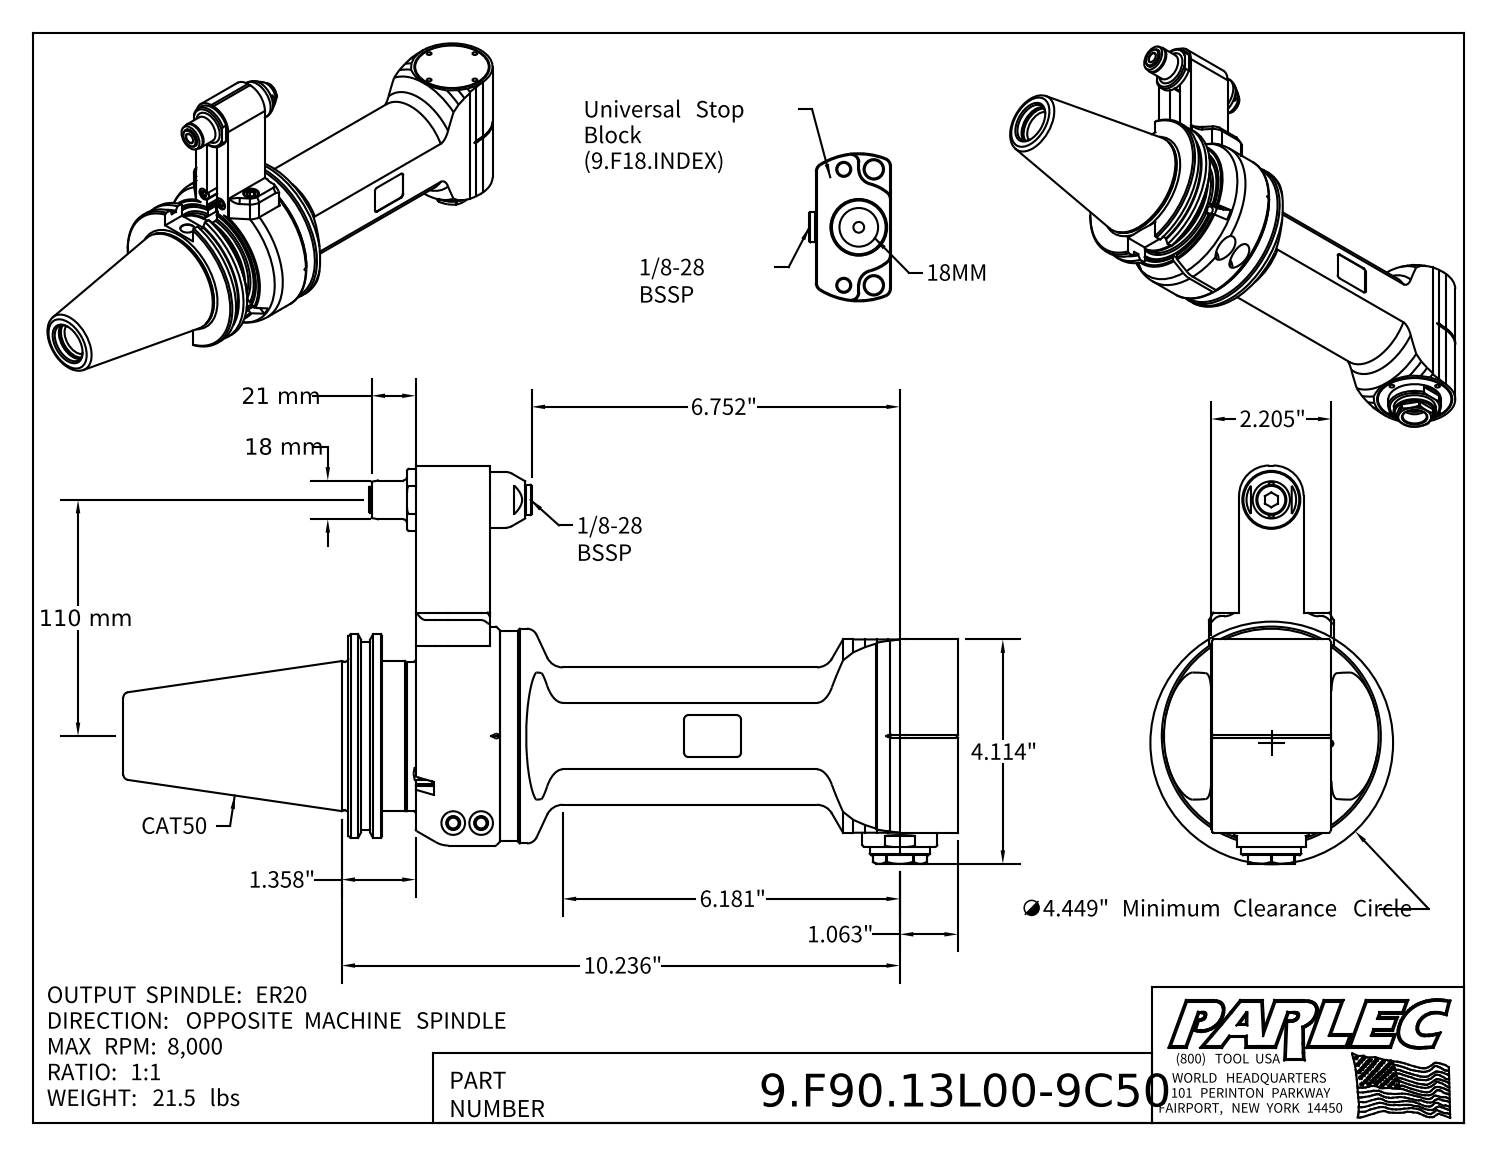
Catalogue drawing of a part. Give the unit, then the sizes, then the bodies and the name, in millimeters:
Units: millimetres
Overall size (bounding box): 388.6 × 185.5 × 102
Round holes (diameter × count): ⌀5 ×7, ⌀3.2 ×4, ⌀6.5 ×3, ⌀8 ×3, ⌀2.6 ×2, ⌀3.3 ×2, ⌀4.2 ×2, ⌀10.4 ×2, ⌀11 ×2, ⌀12.5 ×2, ⌀29 ×2, ⌀3 ×1
Round bosses / shafts (diameter × count): ⌀18 ×2, ⌀12 ×2, ⌀10 ×2, ⌀2.5 ×2, ⌀102 ×1, ⌀100 ×1, ⌀98.4 ×1, ⌀98 ×1
Partial cylindrical surfaces — rounded edges, fillets, slot ends (radius × count): R1 ×14, R2 ×12, R3 ×6, R4 ×4, R0.4 ×2, R0.5 ×2, R8 ×2, R14 ×2
Main face-to-face distances: 32, 13, 56, 43, 54.9, 23, 1, 39.5, 8.5, 70.8
Hole centre spacings: 21.5, 30.4, 7, 21.5, 43, 50.6, 53.6, 60.5
Volume: 1 577 000 mm³ · Surface area: 191 500 mm²
Bodies: 5 solids, 556 faces (227 planar, 160 cylindrical, 169 other)
Part name (STEP PRODUCT): 9.F90.13L00-9C50; 9_GA11C_451 (Type 1, Cat50, 110mm); 9_F90_13L00
STEP written by: Autodesk Inventor 2022 (AUTOMOTIVE_DESIGN)
